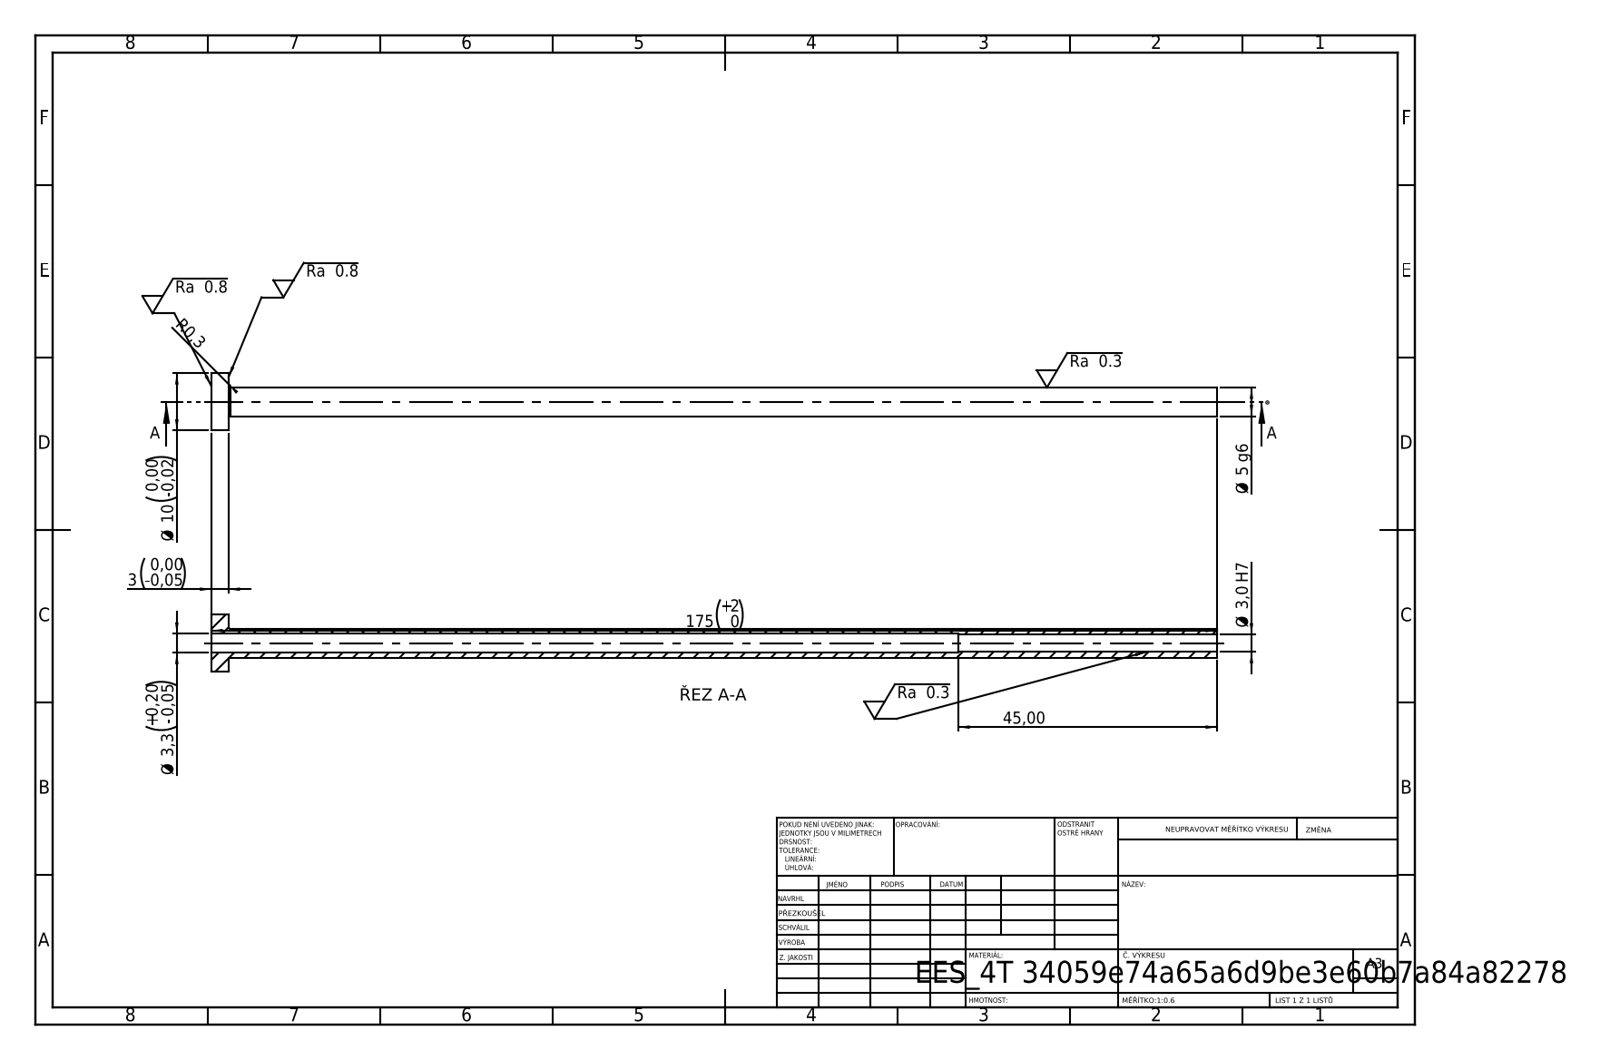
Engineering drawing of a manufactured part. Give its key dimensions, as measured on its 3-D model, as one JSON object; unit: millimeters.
{"step_written_by": "SolidWorks 2019 (CONFIG_CONTROL_DESIGN)", "units": "millimeters", "bodies": {"solids": 1, "faces": 14, "planar": 4, "cylindrical": 8, "other": 2}, "overall_size": [175, 10, 10], "volume_mm3": 2183, "surface_area_mm2": 4709, "round_holes": [[3, 1], [3.3, 1]], "round_bosses_or_shafts": [[10, 1], [5, 1]], "face_to_face_distances": [3, 175, 172, 130, 127, 45]}
